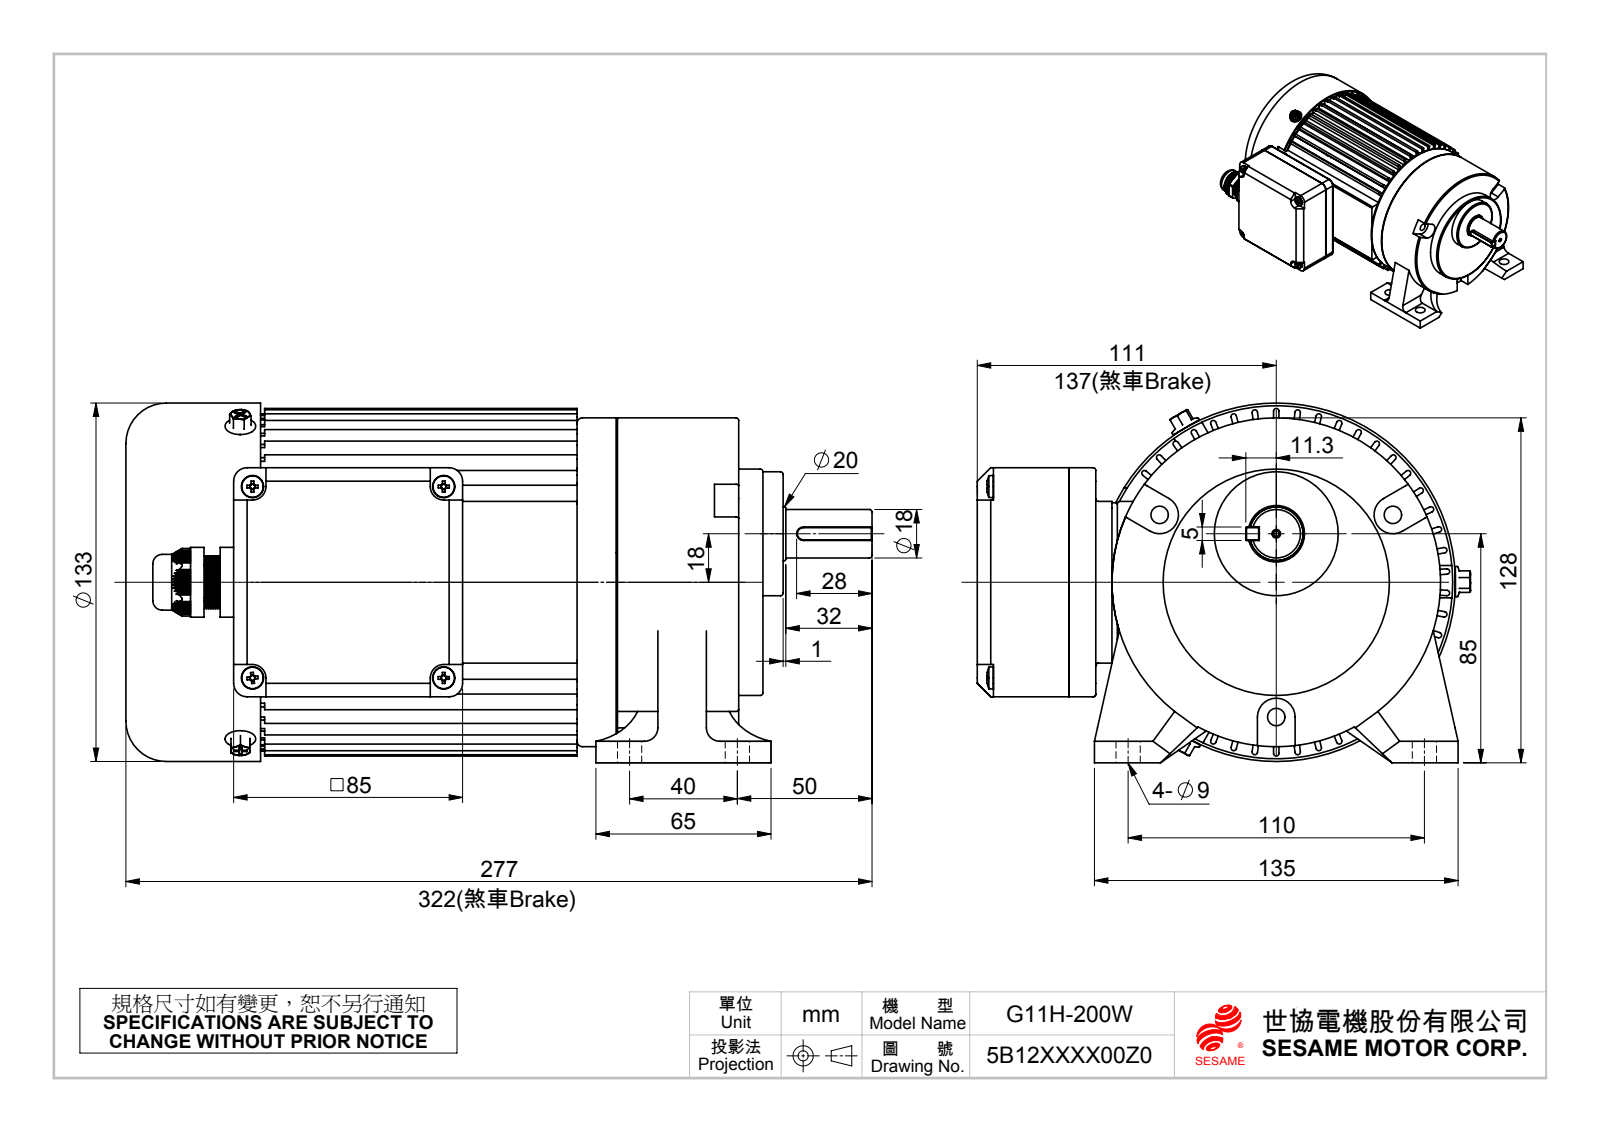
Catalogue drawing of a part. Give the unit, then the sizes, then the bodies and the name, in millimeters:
Units: millimetres
Overall size (bounding box): 277 × 183.11 × 133.5
Round holes (diameter × count): ⌀5 ×11, ⌀3.3 ×9, ⌀8 ×4, ⌀9 ×4, ⌀4.2 ×3, ⌀6.5 ×3, ⌀11 ×3, ⌀2 ×1, ⌀7.5 ×1, ⌀10.8 ×1, ⌀16.5 ×1, ⌀20 ×1
Round bosses / shafts (diameter × count): ⌀8.3 ×4, ⌀4 ×4, ⌀5 ×3, ⌀133 ×1, ⌀131 ×1, ⌀122 ×1, ⌀118 ×1, ⌀110.09 ×1
Partial cylindrical surfaces — rounded edges, fillets, slot ends (radius × count): R1 ×76, R5 ×10, R1.03 ×8, R2.75 ×6, R2 ×4, R2.55 ×4, R3.55 ×4, R22.5 ×4
Main face-to-face distances: 2, 18, 10, 3, 117, 140, 150, 110, 23, 13
Hole centre spacings: 45, 71, 50, 86.6, 11, 11.5, 14.6, 14.79
Volume: 2 632 000 mm³ · Surface area: 410 425 mm²
Bodies: 19 solids, 2670 faces (823 planar, 841 cylindrical, 1006 other)
Part name (STEP PRODUCT): 5x5xL_28L; M200C2A; 油封20x35x7; (標準品)G11H200W(5B12XXX100)(減速比共用) (+8 more)
STEP written by: SolidWorks 2010 (CONFIG_CONTROL_DESIGN)
